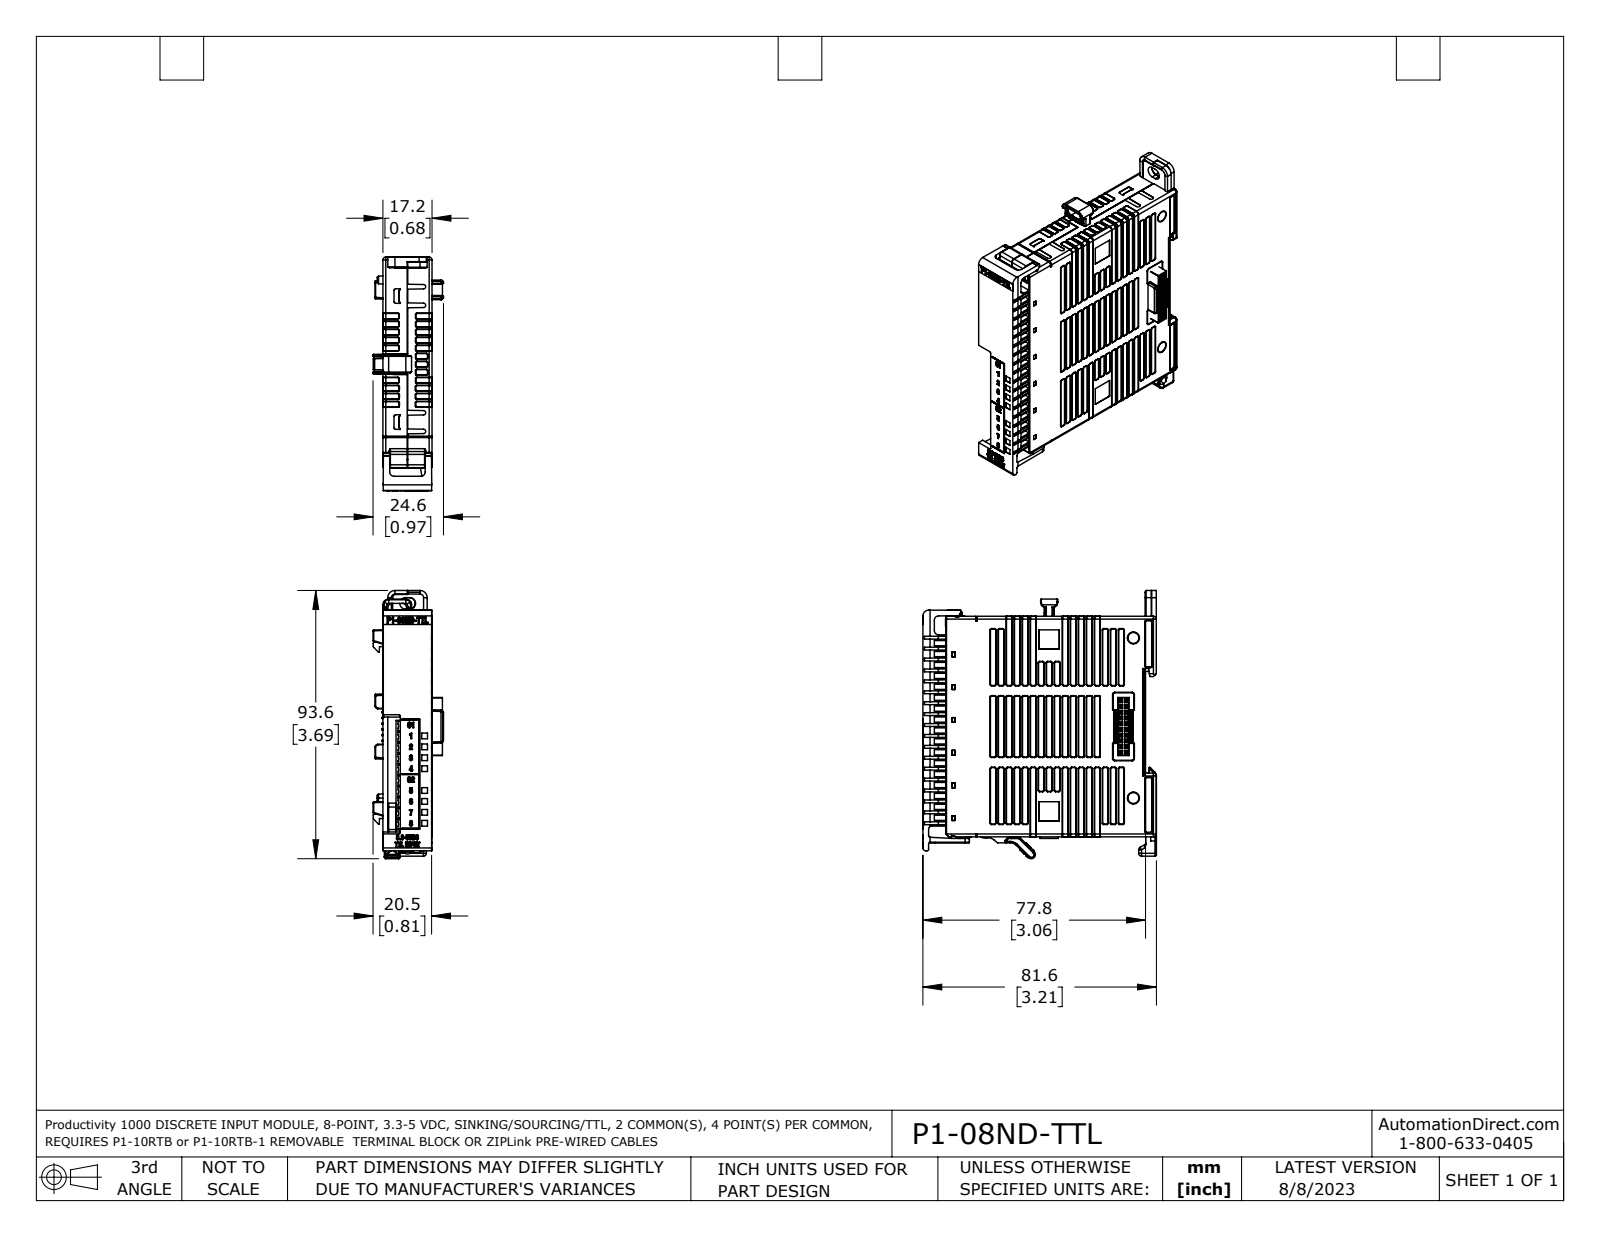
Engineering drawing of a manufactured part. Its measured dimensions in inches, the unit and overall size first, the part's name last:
Units: inches
Overall size (bounding box): 3.686 × 3.212 × 0.969
Round holes (diameter × count): ⌀0.01 ×20, ⌀0.024 ×8, ⌀0.049 ×1
Round bosses / shafts (diameter × count): ⌀0.043 ×2
Partial cylindrical surfaces — rounded edges, fillets, slot ends (radius × count): R0.01 ×207, R0.02 ×139, R0.039 ×58, R0.079 ×12, R0.059 ×11, R0.059 ×10, R0.008 ×8, R0.03 ×8
Main face-to-face distances: 0.674, 0.675, 0.079, 0.672, 0.315, 2.746, 3.061, 0.236, 0.071, 0.157
Hole centre spacings: 0.079, 0.157, 0.176, 0.236, 0.315, 0.394, 0.402, 0.111
Volume: 5.542 in³ · Surface area: 45.9 in²
Bodies: 6 solids, 4526 faces (2426 planar, 1039 cylindrical, 1061 other)
Part name (STEP PRODUCT): P1-04ADL-1 Coord 1 WO Face nc ext2Bcc BODY W P1-08ND-TTL WO CAP SEPERATED 1 DIN Coord sr1 fxt
STEP written by: SolidWorks 2021 (AUTOMOTIVE_DESIGN)
